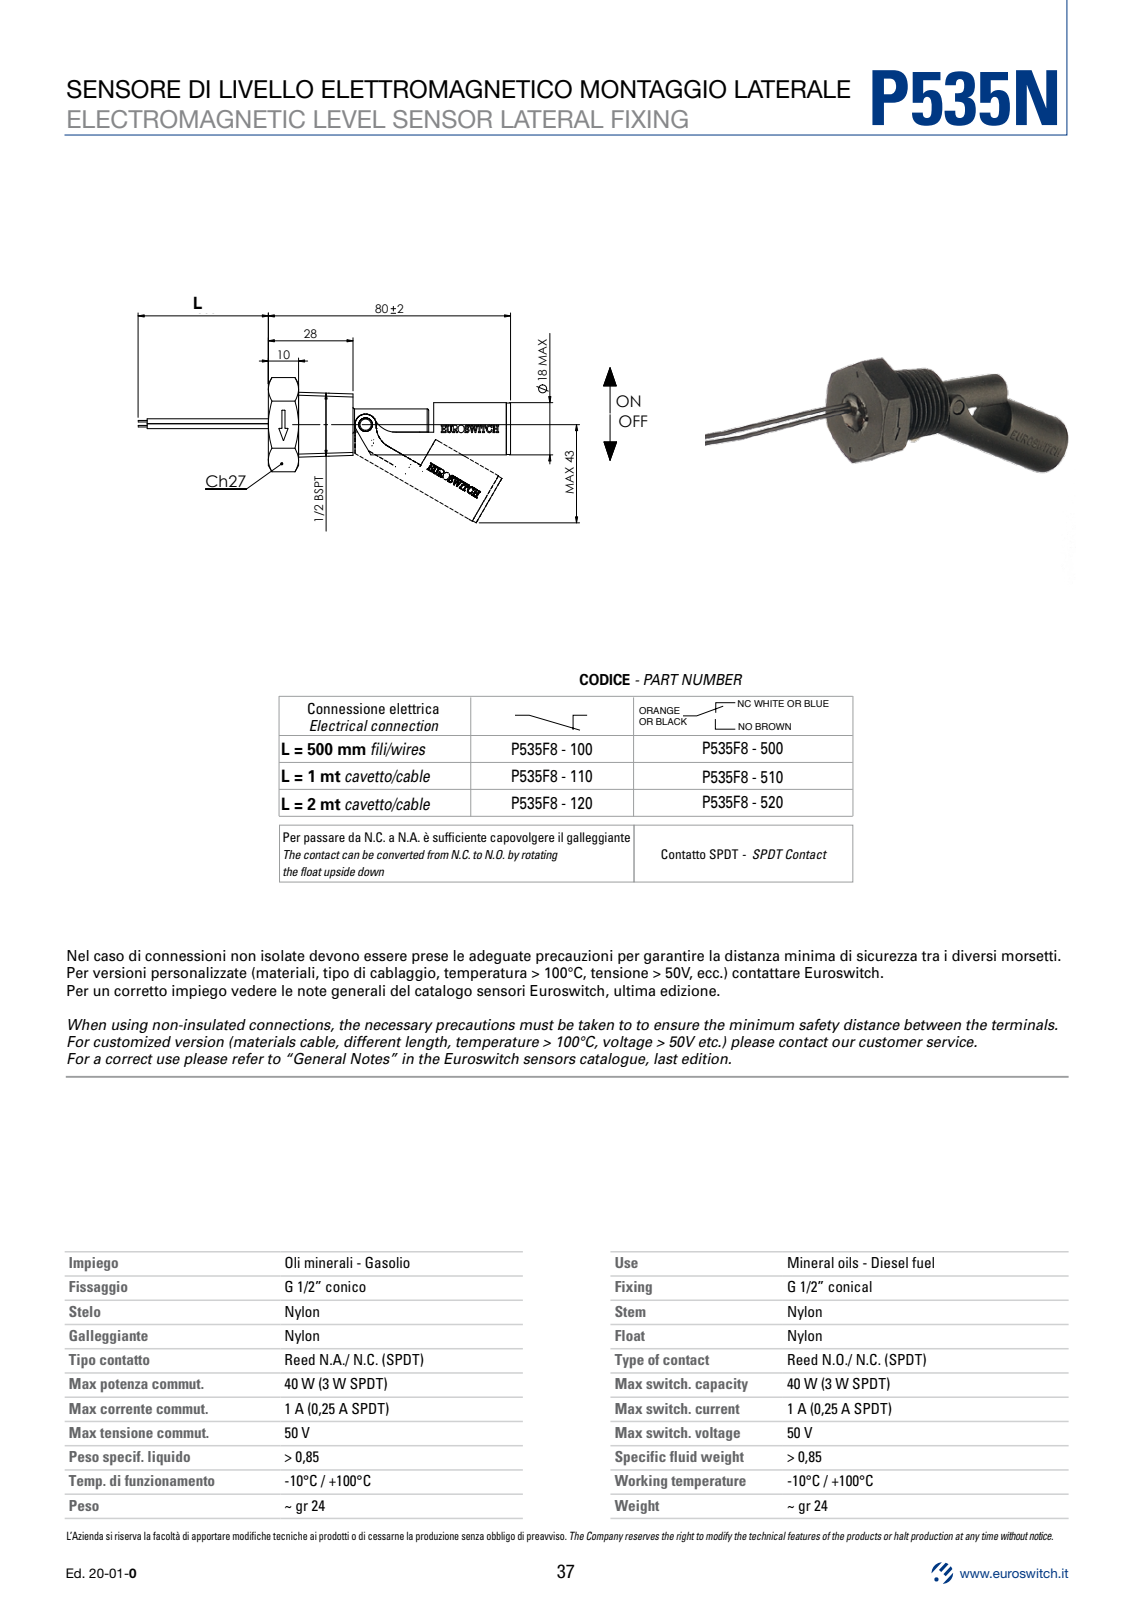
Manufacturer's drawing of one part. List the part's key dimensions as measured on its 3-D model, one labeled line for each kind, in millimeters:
Part name (STEP PRODUCT): P535AH-100
STEP written by: SolidWorks 2019 (AUTOMOTIVE_DESIGN)
Units: millimetres
Bodies: 0 solids, 473 faces (321 planar, 58 cylindrical, 94 other)
Overall size (bounding box): 120.24 × 48.07 × 27
Round holes (diameter × count): ⌀4.5 ×1
Round bosses / shafts (diameter × count): ⌀1.6 ×2, ⌀0.5 ×2, ⌀17.3 ×1, ⌀17 ×1, ⌀9.6 ×1, ⌀3.7 ×1
Partial cylindrical surfaces — rounded edges, fillets, slot ends (radius × count): R0.1 ×5, R3.5 ×1, R5.2 ×1, R7.4 ×1, R8 ×1, R8.65 ×1
Main face-to-face distances: 27, 28, 18, 10, 25.4, 7.65, 19.35, 0.5, 25, 43
